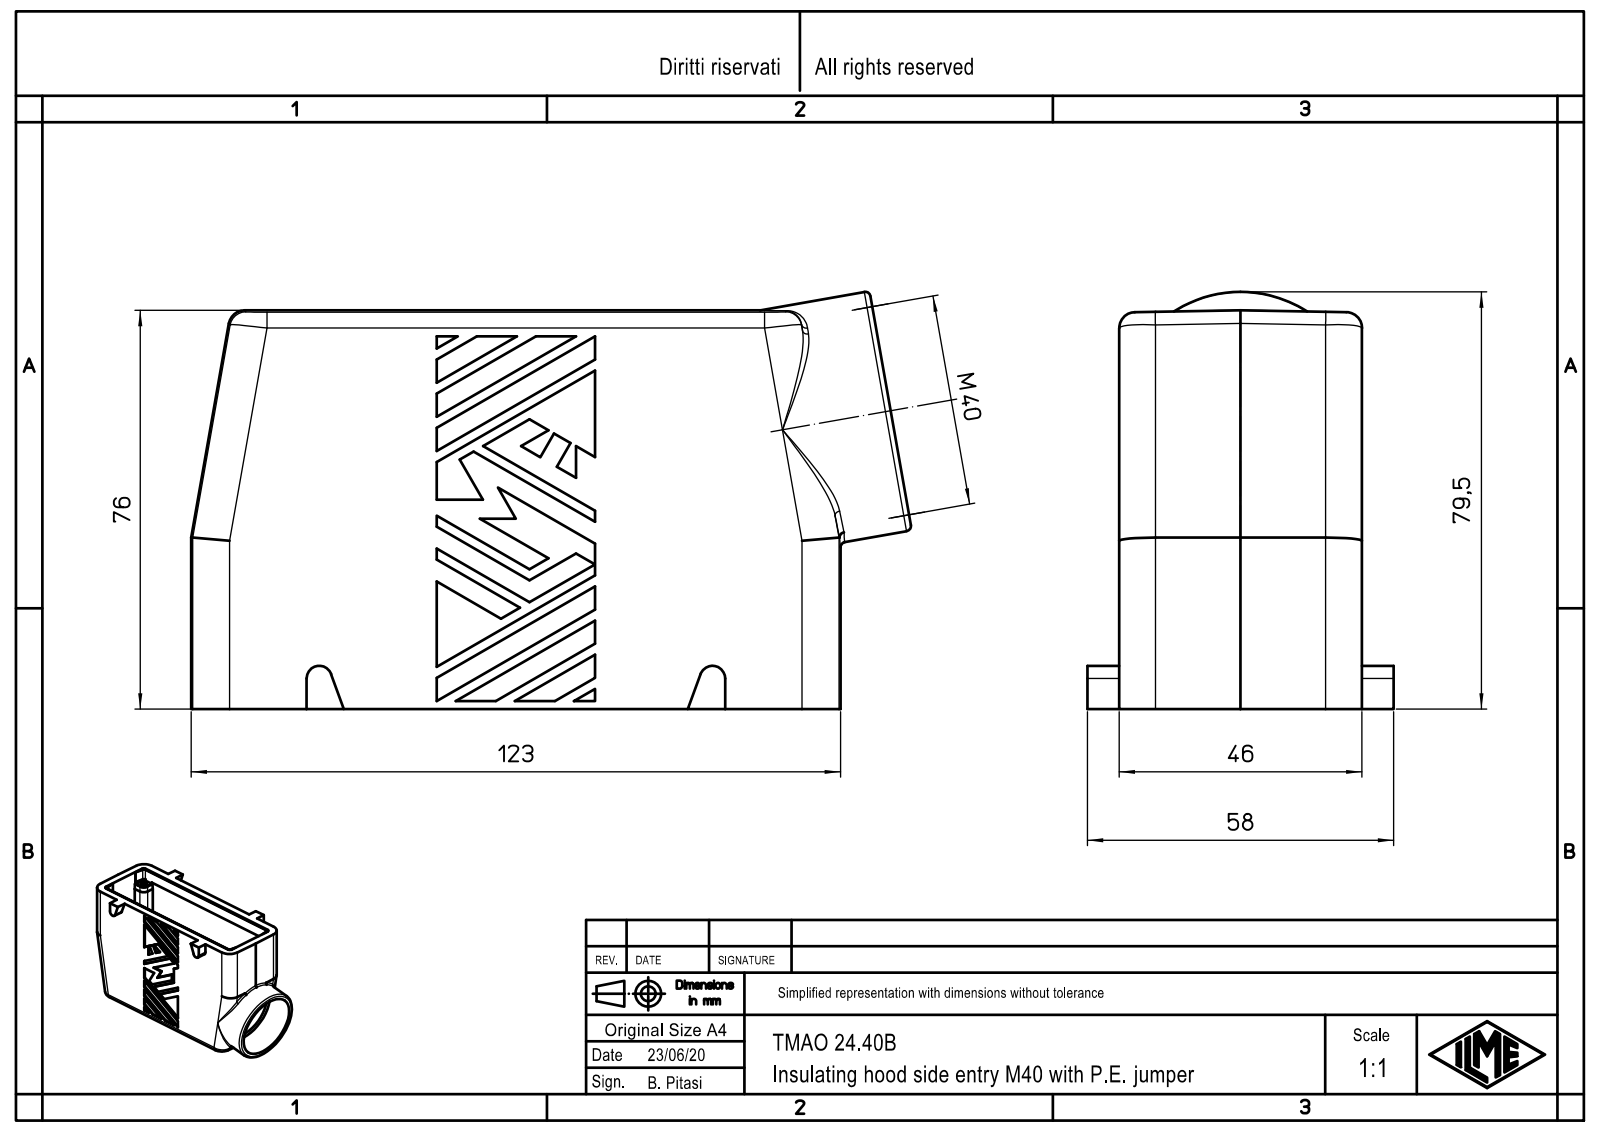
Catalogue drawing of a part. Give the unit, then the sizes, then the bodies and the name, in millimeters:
Units: millimetres
Overall size (bounding box): 136.34 × 78.98 × 58
Round holes (diameter × count): ⌀3 ×4, ⌀3.5 ×4, ⌀34 ×1, ⌀40 ×1
Round bosses / shafts (diameter × count): ⌀4.8 ×4, ⌀46 ×1
Partial cylindrical surfaces — rounded edges, fillets, slot ends (radius × count): R1.5 ×12, R7 ×8, R3 ×6, R1.3 ×4, R1.6 ×4, R2 ×4, R3.5 ×4, R2.4 ×2
Main face-to-face distances: 46, 0.5, 45.5, 69.99, 5.6, 39.4, 40.2, 5.3, 5.8, 39.7
Hole centre spacings: 27, 104, 107.45
Volume: 155 172 mm³ · Surface area: 62 402 mm²
Bodies: 1 solid, 471 faces (300 planar, 83 cylindrical, 88 other)
Part name (STEP PRODUCT): TMAO_24.40B
STEP written by: Creo Elements/Direct Modeling 20.1B 02-Apr-2019 (C) Parametric Technology GmbH (AUTOMOTIVE_DESIGN)
